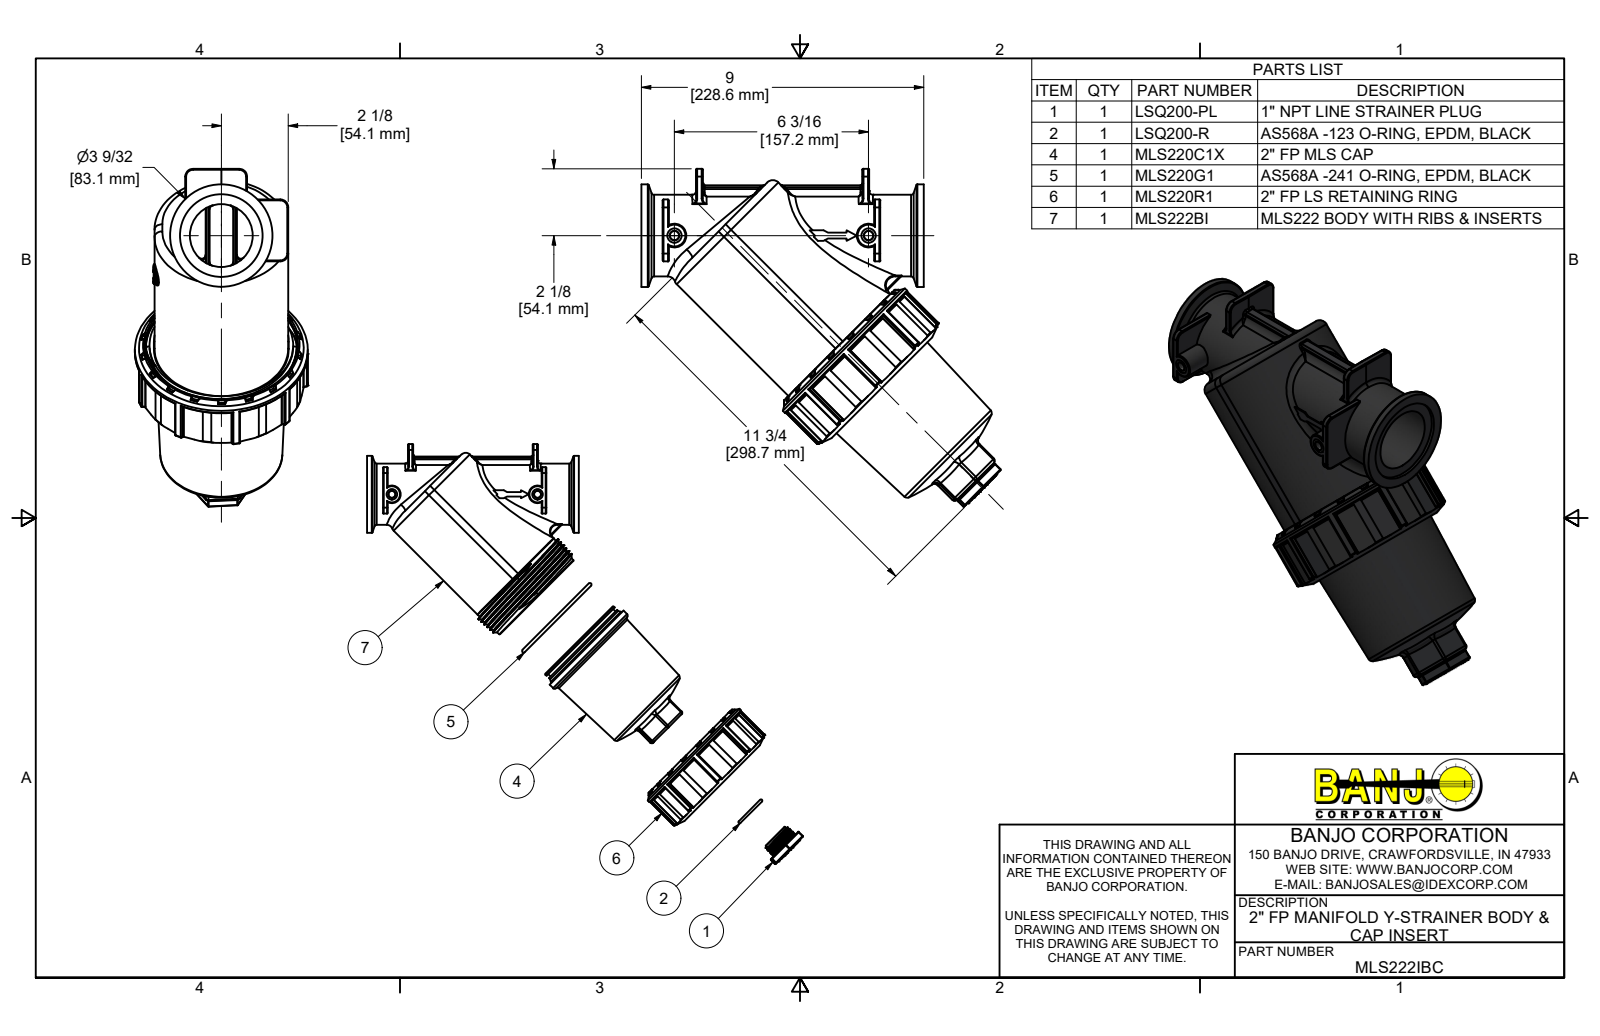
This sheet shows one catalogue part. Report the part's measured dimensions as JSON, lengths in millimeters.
{"part_name": "MLS222IBC; MLS222BI; MLS222B; V25022 (+6 more)", "step_written_by": "Autodesk Inventor 2022 (AUTOMOTIVE_DESIGN)", "units": "millimeters", "bodies": {"solids": 9, "faces": 3337, "planar": 1484, "cylindrical": 544, "other": 1309}, "overall_size": [290.9, 273.4, 140], "volume_mm3": 1339000, "surface_area_mm2": 361200, "round_holes": [[7.5, 2], [7.8, 2], [8.3, 1], [11.5, 1], [11.7, 1], [16.3, 1], [19.1, 1], [25.4, 1], [29.9, 1], [50.8, 1], [66.8, 1], [89.7, 1]], "round_bosses_or_shafts": [[12.7, 2], [11.6, 2], [140, 1], [133.4, 1], [113, 1], [107.1, 1], [104.1, 1], [99.2, 1]], "partial_cylinders_radius": [[0.8, 76], [0.3, 36], [1.5, 16], [2.3, 12], [6.4, 8], [3.2, 6], [3, 3], [0.5, 2]], "face_to_face_distances": [2.5, 226.1, 7.6, 228.6, 147.5, 155.2, 134.6, 5.1, 171.2, 27.8], "hole_center_spacings": [34.3, 64.1, 94.6, 97.7, 106.5, 157.2]}
